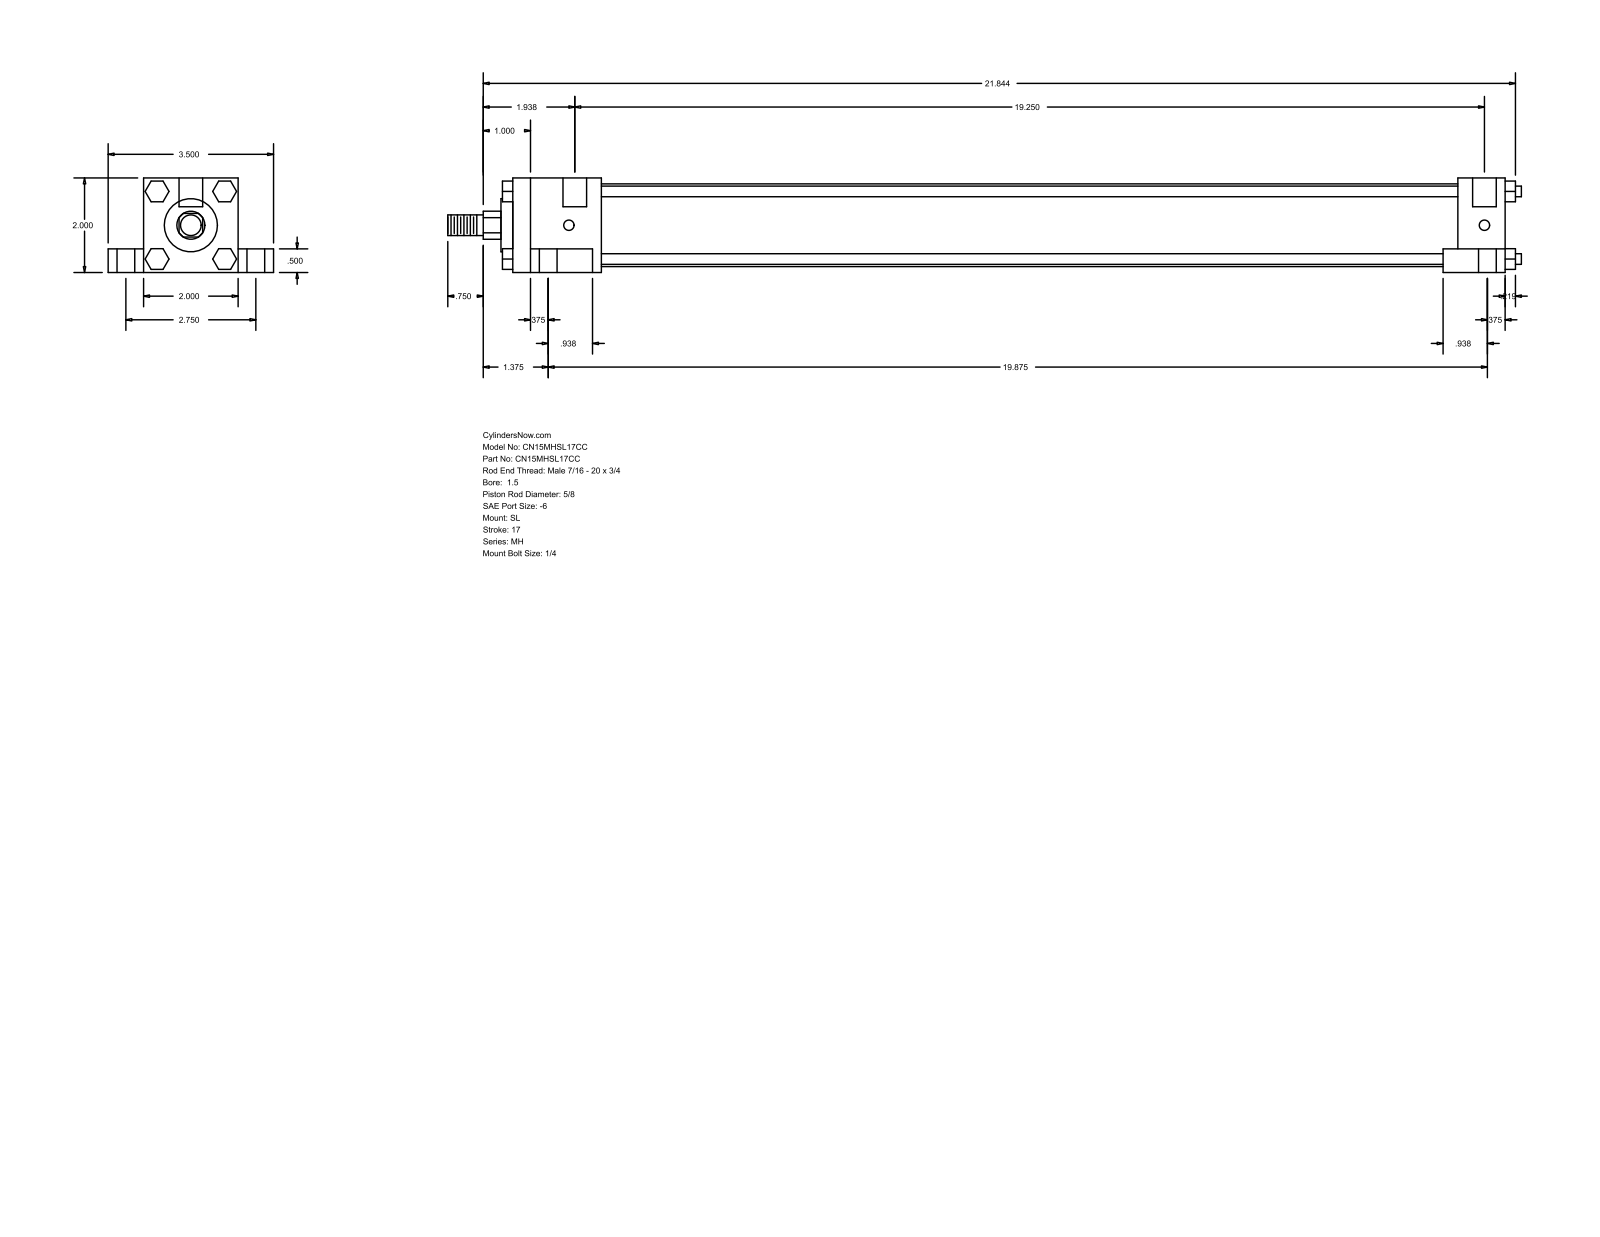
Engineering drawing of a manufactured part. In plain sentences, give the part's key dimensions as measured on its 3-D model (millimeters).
The part is named "MH_SL__0150_0.625". Its 3-D file was written by "GSSL Pune (CONFIG_CONTROL_DESIGN)". It is 0 solids with 148 faces: 112 planar, 36 cylindrical and 0 other. Overall it measures 577.06 by 88.9 by 50.8 millimeters. Round holes: 4 of diameter 5.56, 4 of diameter 9.53, 4 of diameter 15.88, 2 of diameter 12.7. Round bosses or shafts: 4 of diameter 5.71, 1 of diameter 44.45, 1 of diameter 28.57, 1 of diameter 15.88, 1 of diameter 11.11. Partial cylindrical surfaces (rounded edges, fillets, slot ends): 1 of radius 7.54. The main face-to-face distances are 50.8, 38.1, 19.05, 12.7, 69.85, 533.39, 9.52, 508, 25.39, 47.62. The hole center spacings are 34.96, 36.65, 37.73, 69.84, 491.78, 492.12, 494.94, 504.45.
